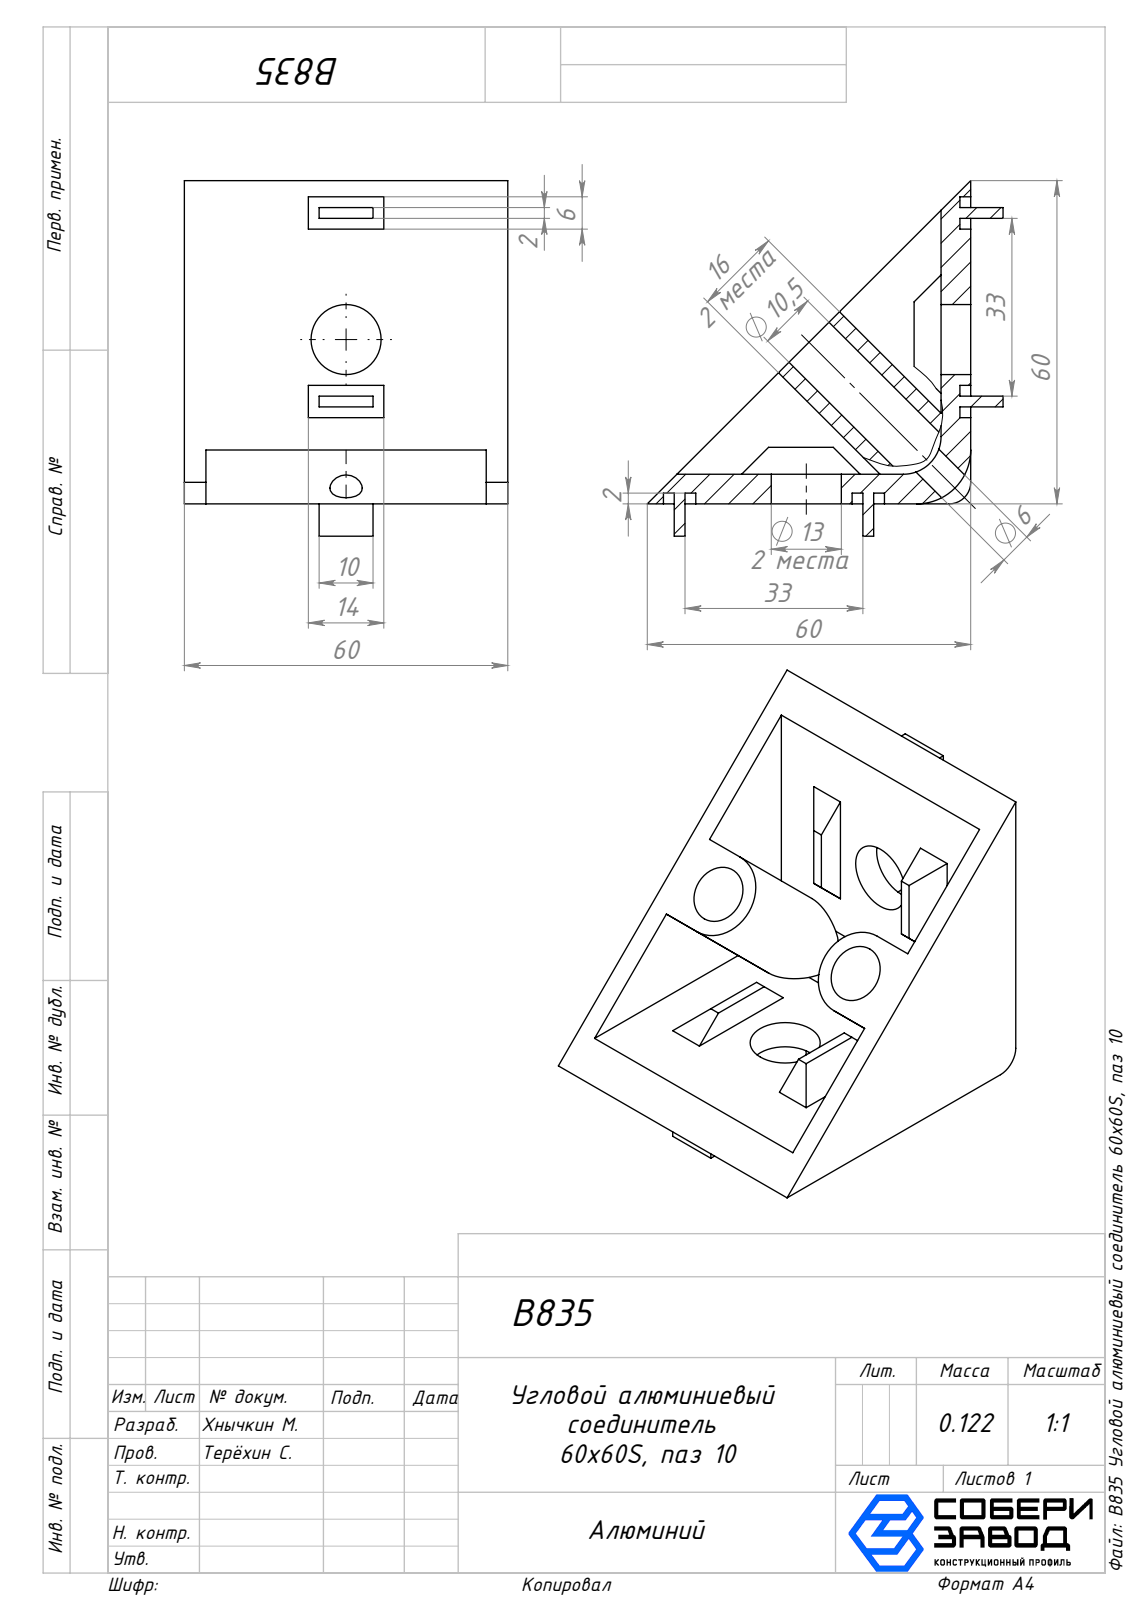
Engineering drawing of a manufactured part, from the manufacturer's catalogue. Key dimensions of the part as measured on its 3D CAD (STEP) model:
Part name (STEP PRODUCT): B835 Угловой алюминиевый соединитель 60х60S, паз 10
STEP written by: SolidWorks 2025 (AUTOMOTIVE_DESIGN)
Units: millimetres
Bodies: 1 solid, 99 faces (81 planar, 18 cylindrical, 0 other)
Overall size (bounding box): 66 × 66 × 60
Volume: 53 304 mm³ · Surface area: 24 327 mm²
Round holes (diameter × count): ⌀10.5 ×2, ⌀13 ×2, ⌀6 ×1
Partial cylindrical surfaces — rounded edges, fillets, slot ends (radius × count): R8 ×2, R4 ×1, R7 ×1, R10 ×1
Main face-to-face distances: 5.5, 60, 4, 56, 2, 52, 16, 35, 15.5, 40.5
Hole centre spacings: 18, 36
